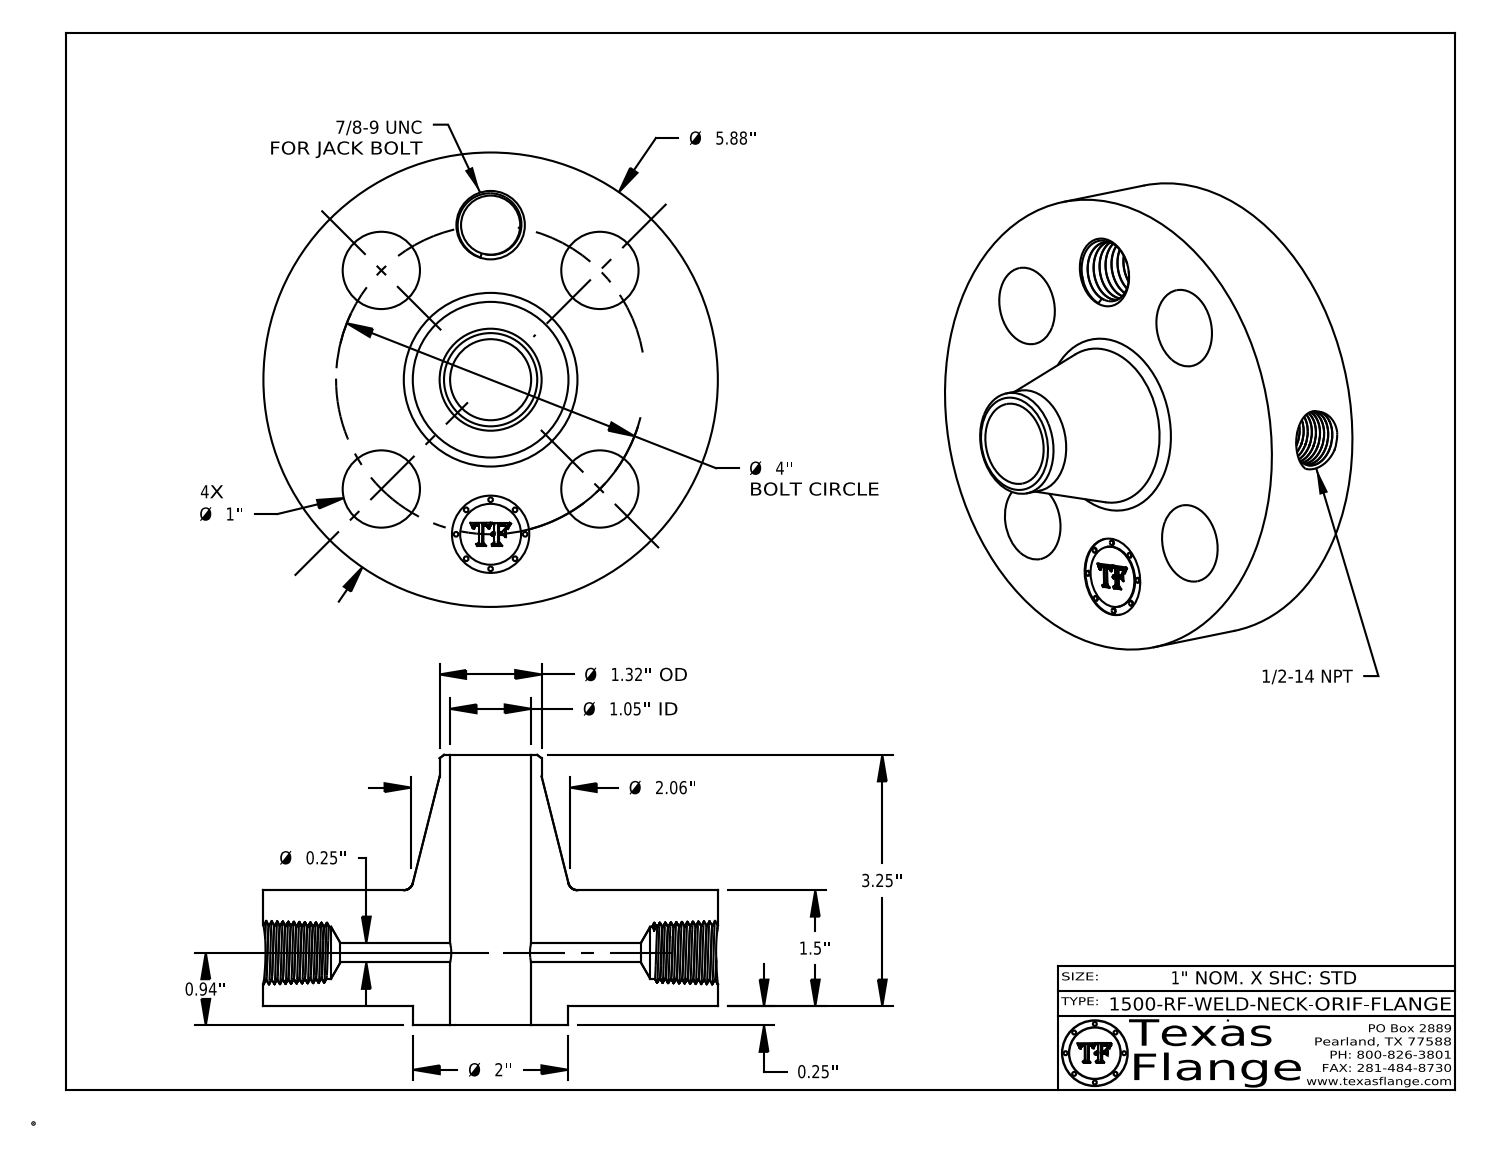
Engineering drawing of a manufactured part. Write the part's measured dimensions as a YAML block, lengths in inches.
part_name: "1500-RF-WELD-NECK"
step_written_by: "CATIA V5 STEP AP214 (AUTOMOTIVE_DESIGN)"
units: inches
bodies: {solids: 1, faces: 749, planar: 369, cylindrical: 82, other: 298}
overall_size: [5.88, 5.88, 3.5]
volume: 35.8
surface_area: 126.4
round_holes:
  - {diameter: 1, count: 5}
  - {diameter: 0.25, count: 1}
  - {diameter: 0.672, count: 1}
  - {diameter: 0.766, count: 1}
  - {diameter: 1.049, count: 1}
round_bosses_or_shafts:
  - {diameter: 0.061, count: 8}
  - {diameter: 5.88, count: 1}
  - {diameter: 2, count: 1}
  - {diameter: 1.32, count: 1}
  - {diameter: 0.788, count: 1}
face_to_face_distances: [1.5, 1.75, 0.25, 1.735, 1.485, 0.015, 3.5, 3.25, 1.765, 0.298]
hole_center_spacings: [2, 1.531, 2.828, 3.695, 4]
